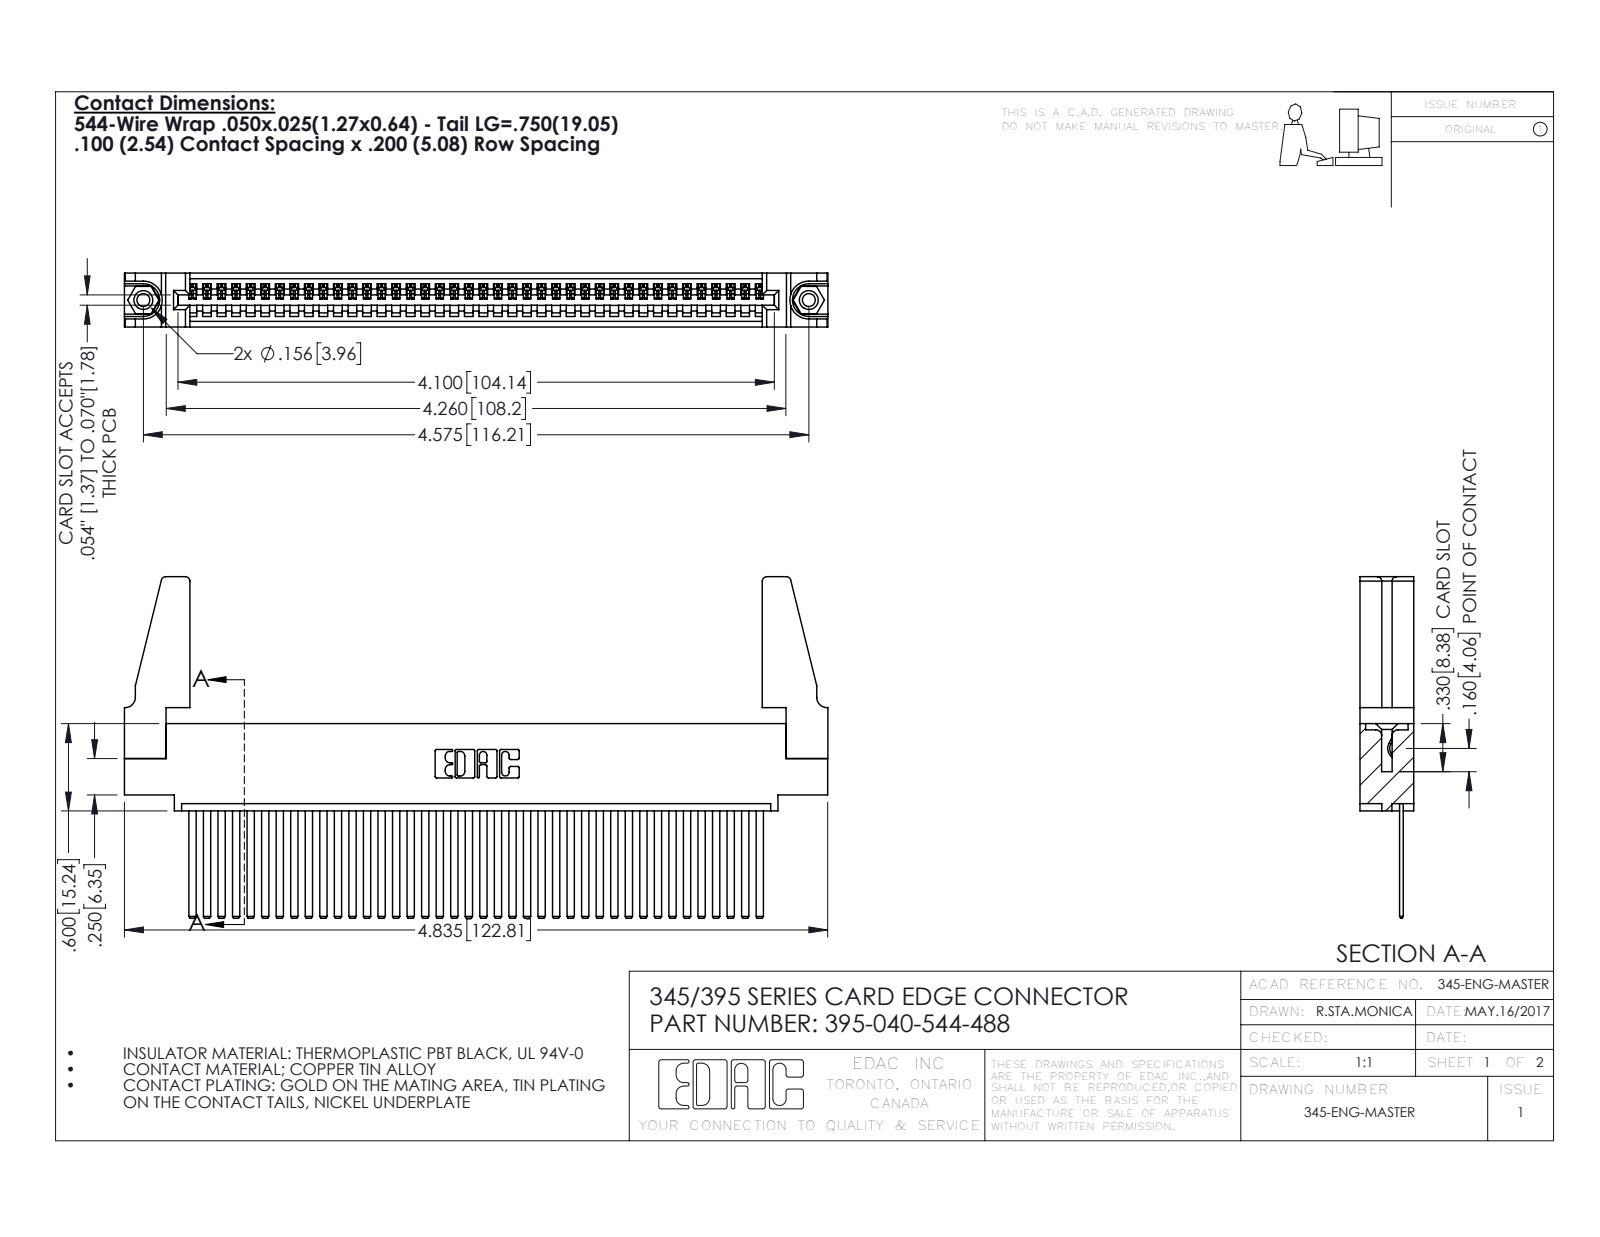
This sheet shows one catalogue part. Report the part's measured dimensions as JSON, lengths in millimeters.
{"part_name": "345-220-078_345-220-088; 345-250-001_345-250-001-102; 395-040-544-488; 345-292-001_345-293-144 (+1 more)", "step_written_by": "SolidWorks 2016 (CONFIG_CONTROL_DESIGN)", "units": "millimeters", "bodies": {"solids": 45, "faces": 2334, "planar": 1596, "cylindrical": 722, "other": 16}, "overall_size": [122.8, 59.6, 9.4], "volume_mm3": 15300, "surface_area_mm2": 20570, "round_holes": [[2.3, 2], [3.2, 2], [4, 2], [1.6, 1]], "round_bosses_or_shafts": [[3.9, 2]], "partial_cylinders_radius": [[0.2, 80], [0.3, 22], [0.8, 8], [0.2, 6], [0.8, 6], [0.7, 3], [0.8, 2], [1, 2]], "face_to_face_distances": [1.8, 7.6, 2.5, 6.9, 0.6, 9.4, 5.1, 5.7, 3.8, 1.8], "hole_center_spacings": [6.9, 110.2, 116.2]}
